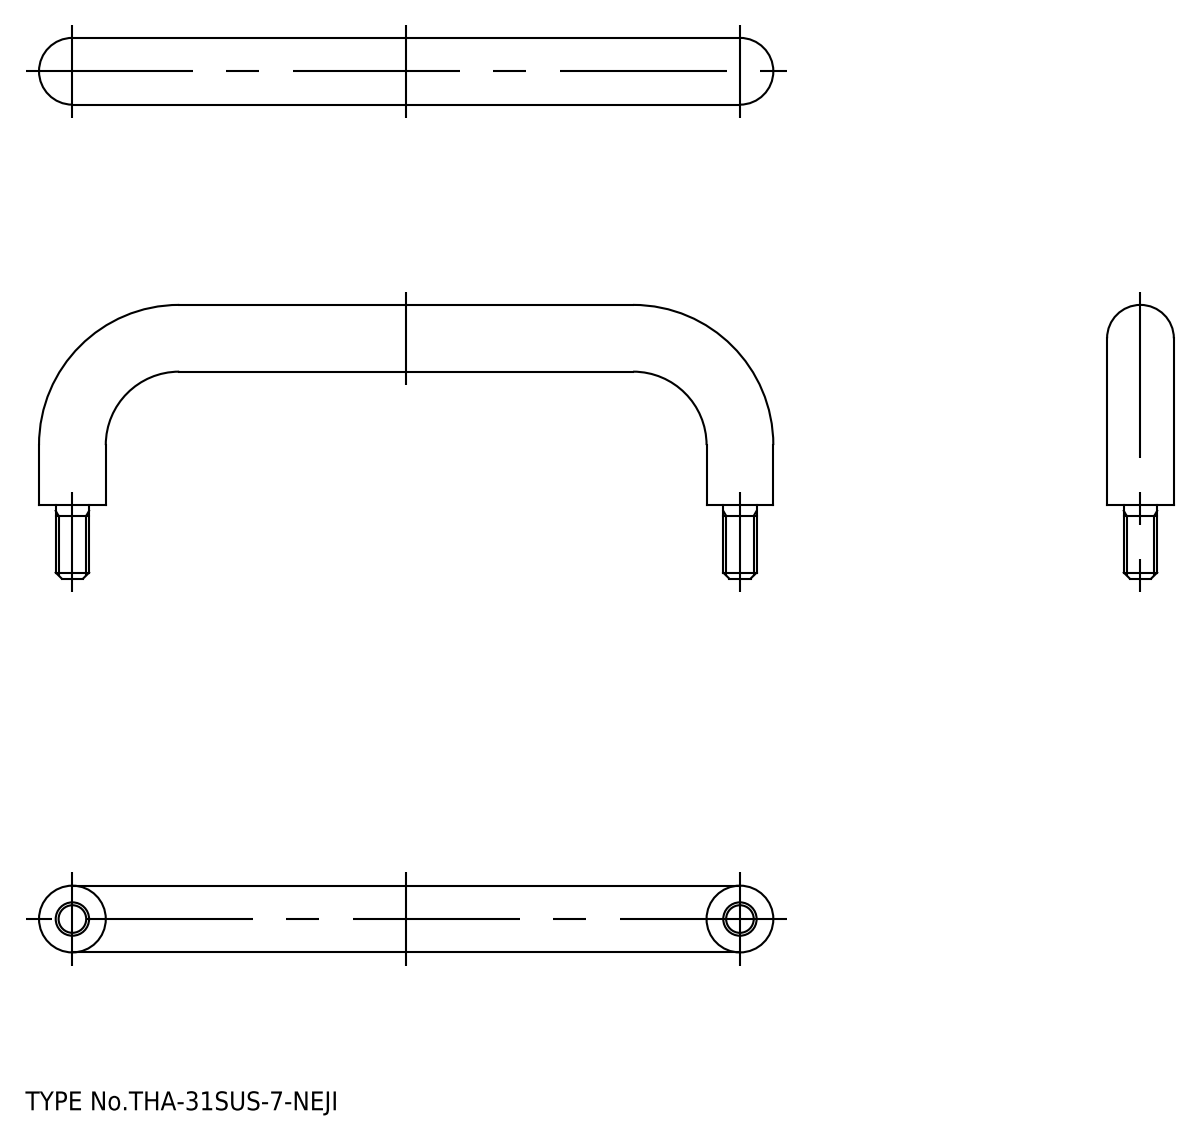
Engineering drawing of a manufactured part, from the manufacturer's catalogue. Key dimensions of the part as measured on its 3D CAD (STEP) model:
STEP written by: spGate 17.5.2 (AUTOMOTIVE_DESIGN)
Units: millimetres
Bodies: 1 solid, 24 faces (4 planar, 12 cylindrical, 8 other)
Overall size (bounding box): 110 × 41 × 10.01
Volume: 11 130 mm³ · Surface area: 4 774 mm²
Round bosses / shafts (diameter × count): ⌀10 ×3, ⌀5 ×2
Main face-to-face distances: 11
